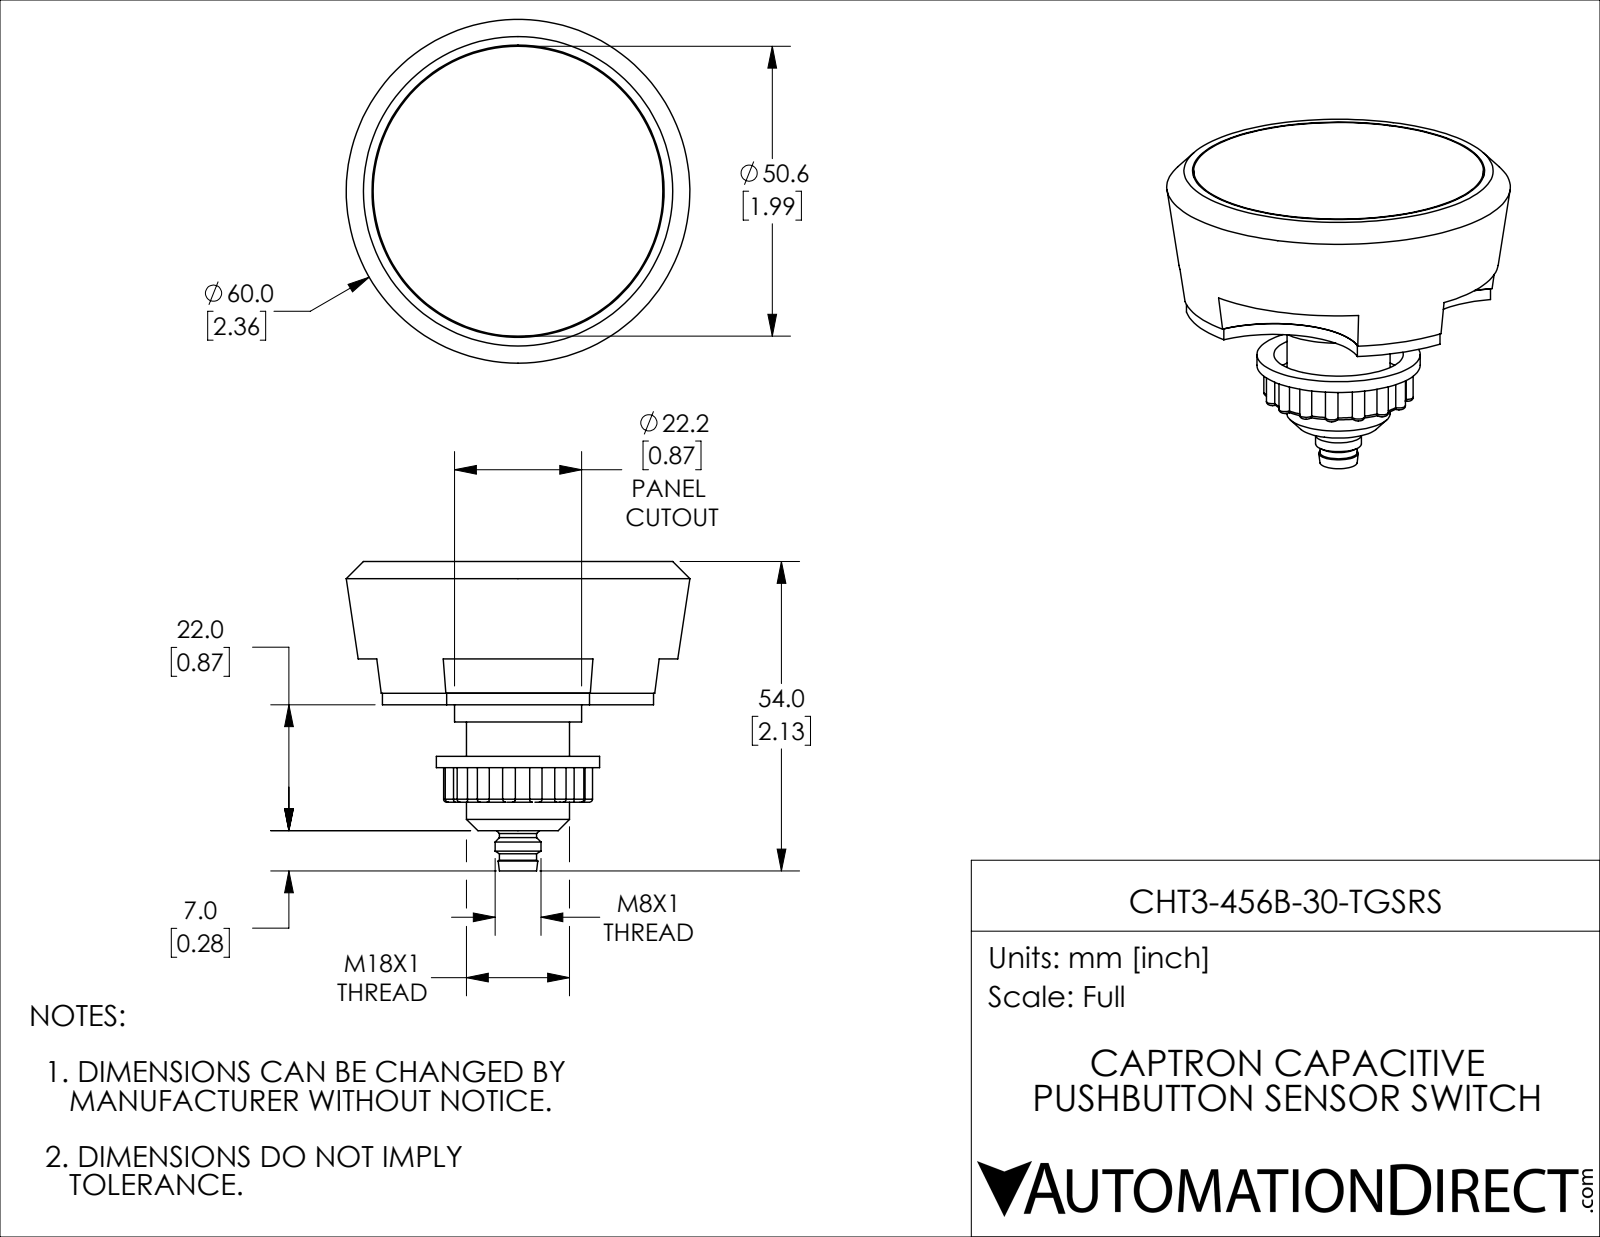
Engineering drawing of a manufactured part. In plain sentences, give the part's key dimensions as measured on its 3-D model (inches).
The part is named "CHT3-456B-30-TGSRS". Its 3-D file was written by "SolidWorks 2019 (CONFIG_CONTROL_DESIGN)". It is 10 solids with 200 faces: 28 planar, 94 cylindrical and 78 other. Overall it measures 2.362 by 2.362 by 2.126 inches. Its volume is 3.853 cubic inches and its surface area 32.45 square inches. Round holes: 1 of diameter 0.669, 1 of diameter 0.89, 1 of diameter 2.008. Round bosses or shafts: 5 of diameter 0.039, 1 of diameter 1.992, 1 of diameter 1.122, 1 of diameter 0.874, 1 of diameter 0.709, 1 of diameter 0.315, 1 of diameter 0.256. Partial cylindrical surfaces (rounded edges, fillets, slot ends): 16 of radius 0.043, 4 of radius 0.591, 2 of radius 0.02, 1 of radius 0.039, 1 of radius 0.114, 1 of radius 0.472, 1 of radius 1.053. The main face-to-face distances are 0.906, 0.091, 0.815, 0.134, 0.772, 0.043, 0.079, 0.984, 0.669, 0.85.
